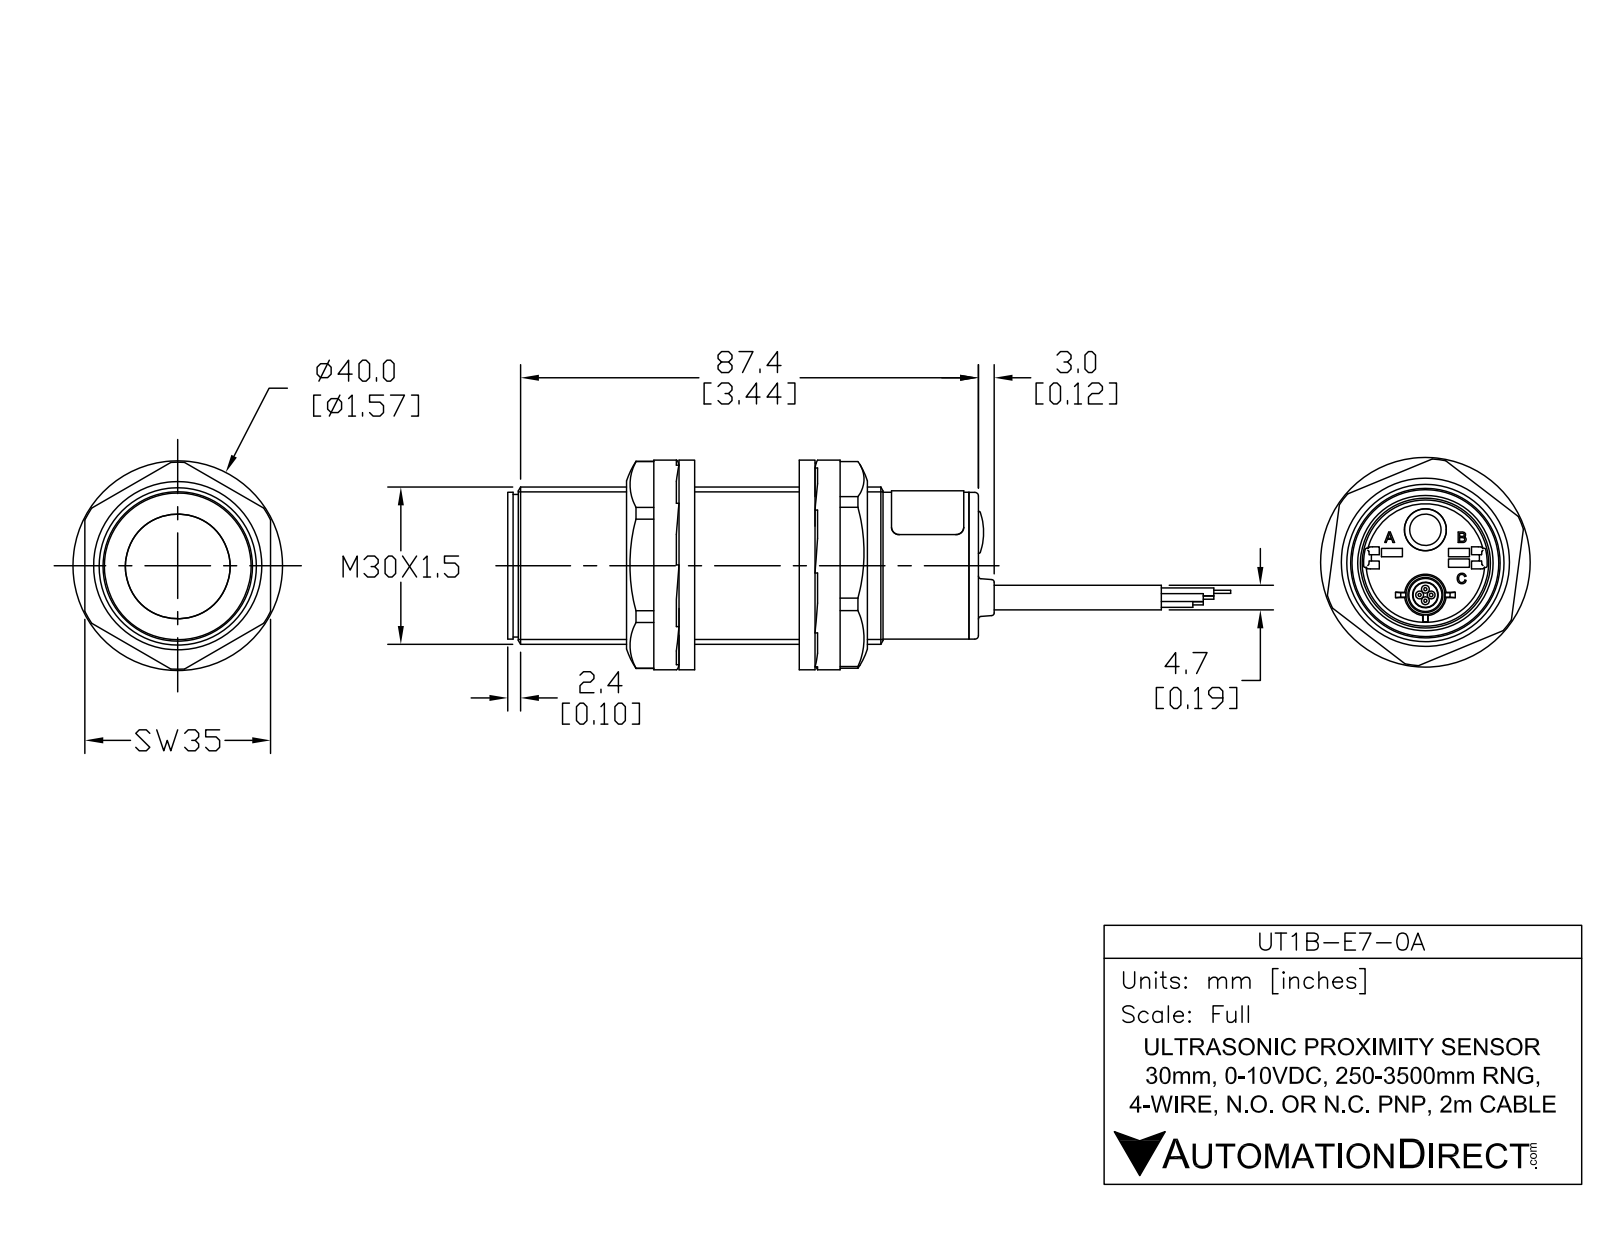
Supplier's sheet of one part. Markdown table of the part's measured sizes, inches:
| quantity | value |
| --- | --- |
| part name | UT1B-E7-0A |
| STEP written by | SolidWorks 2017 (AUTOMOTIVE_DESIGN) |
| units | inches |
| bodies | 5 solids, 48 faces (13 planar, 18 cylindrical, 17 other) |
| overall size | 5.039 × 1.181 × 1.181 |
| volume | 3.762 in³ |
| surface area | 19.85 in² |
| round holes (diameter × count) | 0.185 × 1, 0.315 × 1, 0.925 × 1 |
| round bosses / shafts (diameter × count) | 1.181 × 1, 1.102 × 1, 1.071 × 1 |
| main face-to-face distances | 3.386, 3.457, 0.071, 0.039, 3.425, 3.496, 0.039, 3.425, 3.496, 0.031 |
| hole center spacings | 0.239, 0.25, 0.49 |
